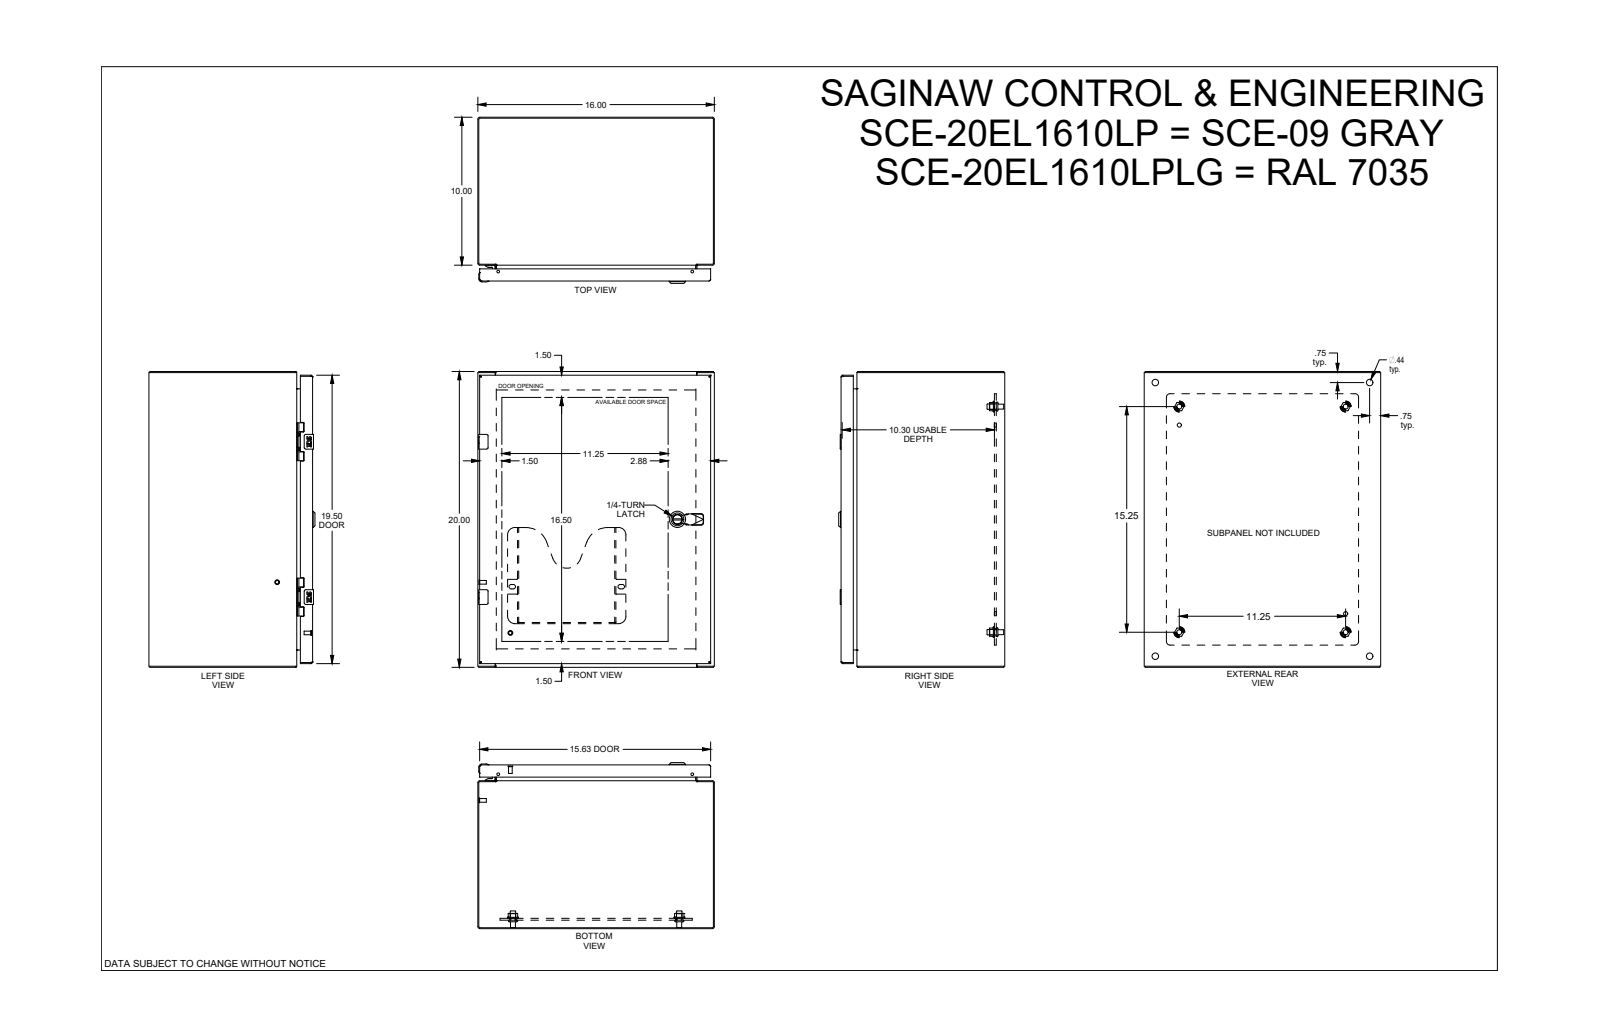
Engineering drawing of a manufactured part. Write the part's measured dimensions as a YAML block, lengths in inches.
part_name: "SCE-20EL1610LP"
step_written_by: "SolidWorks 2021 (AUTOMOTIVE_DESIGN)"
units: inches
bodies: {solids: 24, faces: 1217, planar: 544, cylindrical: 474, other: 199}
overall_size: [20, 16, 11.935]
volume: 154.7
surface_area: 3789
round_holes:
  - {diameter: 0.172, count: 4}
  - {diameter: 0.205, count: 4}
  - {diameter: 0.244, count: 4}
  - {diameter: 0.375, count: 4}
  - {diameter: 0.437, count: 4}
  - {diameter: 0.5, count: 4}
  - {diameter: 0.04, count: 2}
  - {diameter: 0.188, count: 2}
  - {diameter: 0.218, count: 2}
  - {diameter: 0.281, count: 2}
  - {diameter: 0.197, count: 1}
  - {diameter: 0.204, count: 1}
round_bosses_or_shafts:
  - {diameter: 0.375, count: 4}
  - {diameter: 0.33, count: 4}
  - {diameter: 0.25, count: 4}
  - {diameter: 0.248, count: 4}
  - {diameter: 0.24, count: 4}
  - {diameter: 1.102, count: 1}
  - {diameter: 0.78, count: 1}
  - {diameter: 0.63, count: 1}
partial_cylinders:
  - {radius: 0.015, count: 24}
  - {radius: 0.04, count: 17}
  - {radius: 0.22, count: 16}
  - {radius: 0.043, count: 12}
  - {radius: 0.118, count: 12}
  - {radius: 0.031, count: 10}
  - {radius: 0.06, count: 9}
  - {radius: 0.062, count: 8}
face_to_face_distances: [0.075, 15.925, 0.06, 10.993, 19.925, 11.068, 11.008, 10.933, 0.125, 0.5]
hole_center_spacings: [0.494, 10.5, 0.984, 1.25, 2.317, 2.319, 2.452, 2.87]
